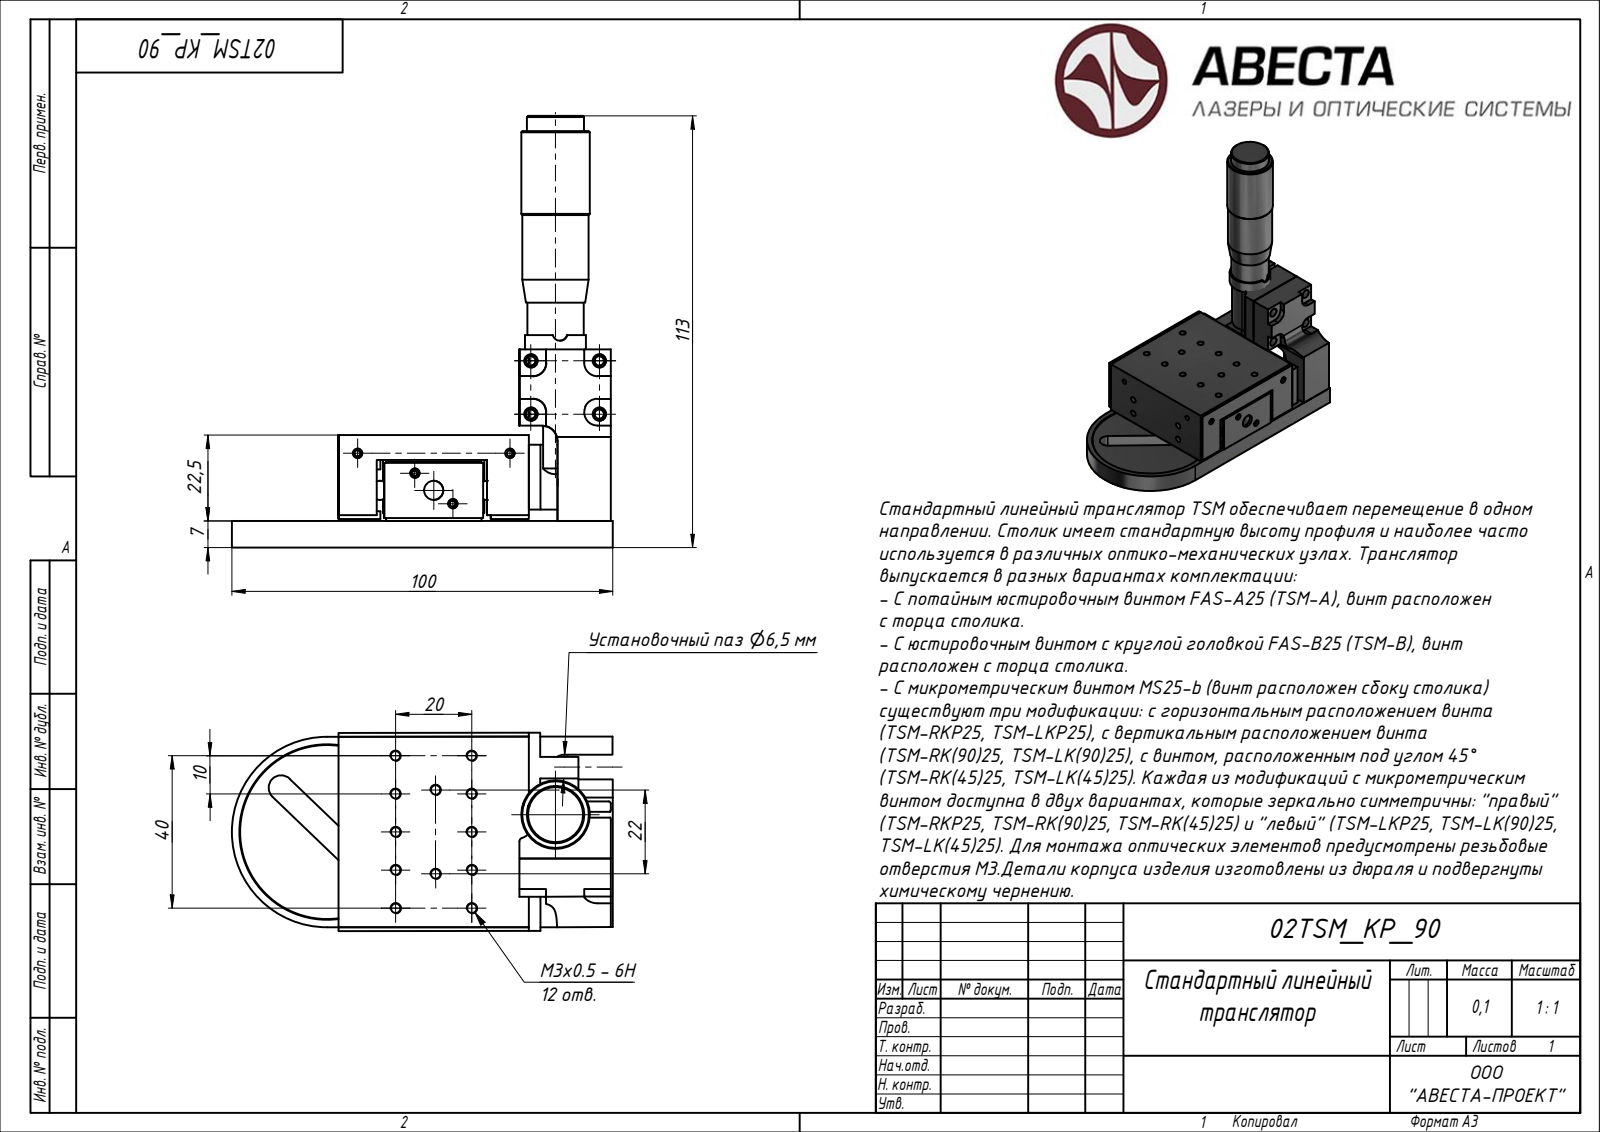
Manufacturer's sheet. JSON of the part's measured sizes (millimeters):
{"step_written_by": "ST-DEVELOPER v15 (AUTOMOTIVE_DESIGN)", "units": "millimeters", "bodies": {"solids": 23, "faces": 811, "planar": 0, "cylindrical": 0, "other": 811}, "overall_size": [113.27, 100.02, 56.03]}
